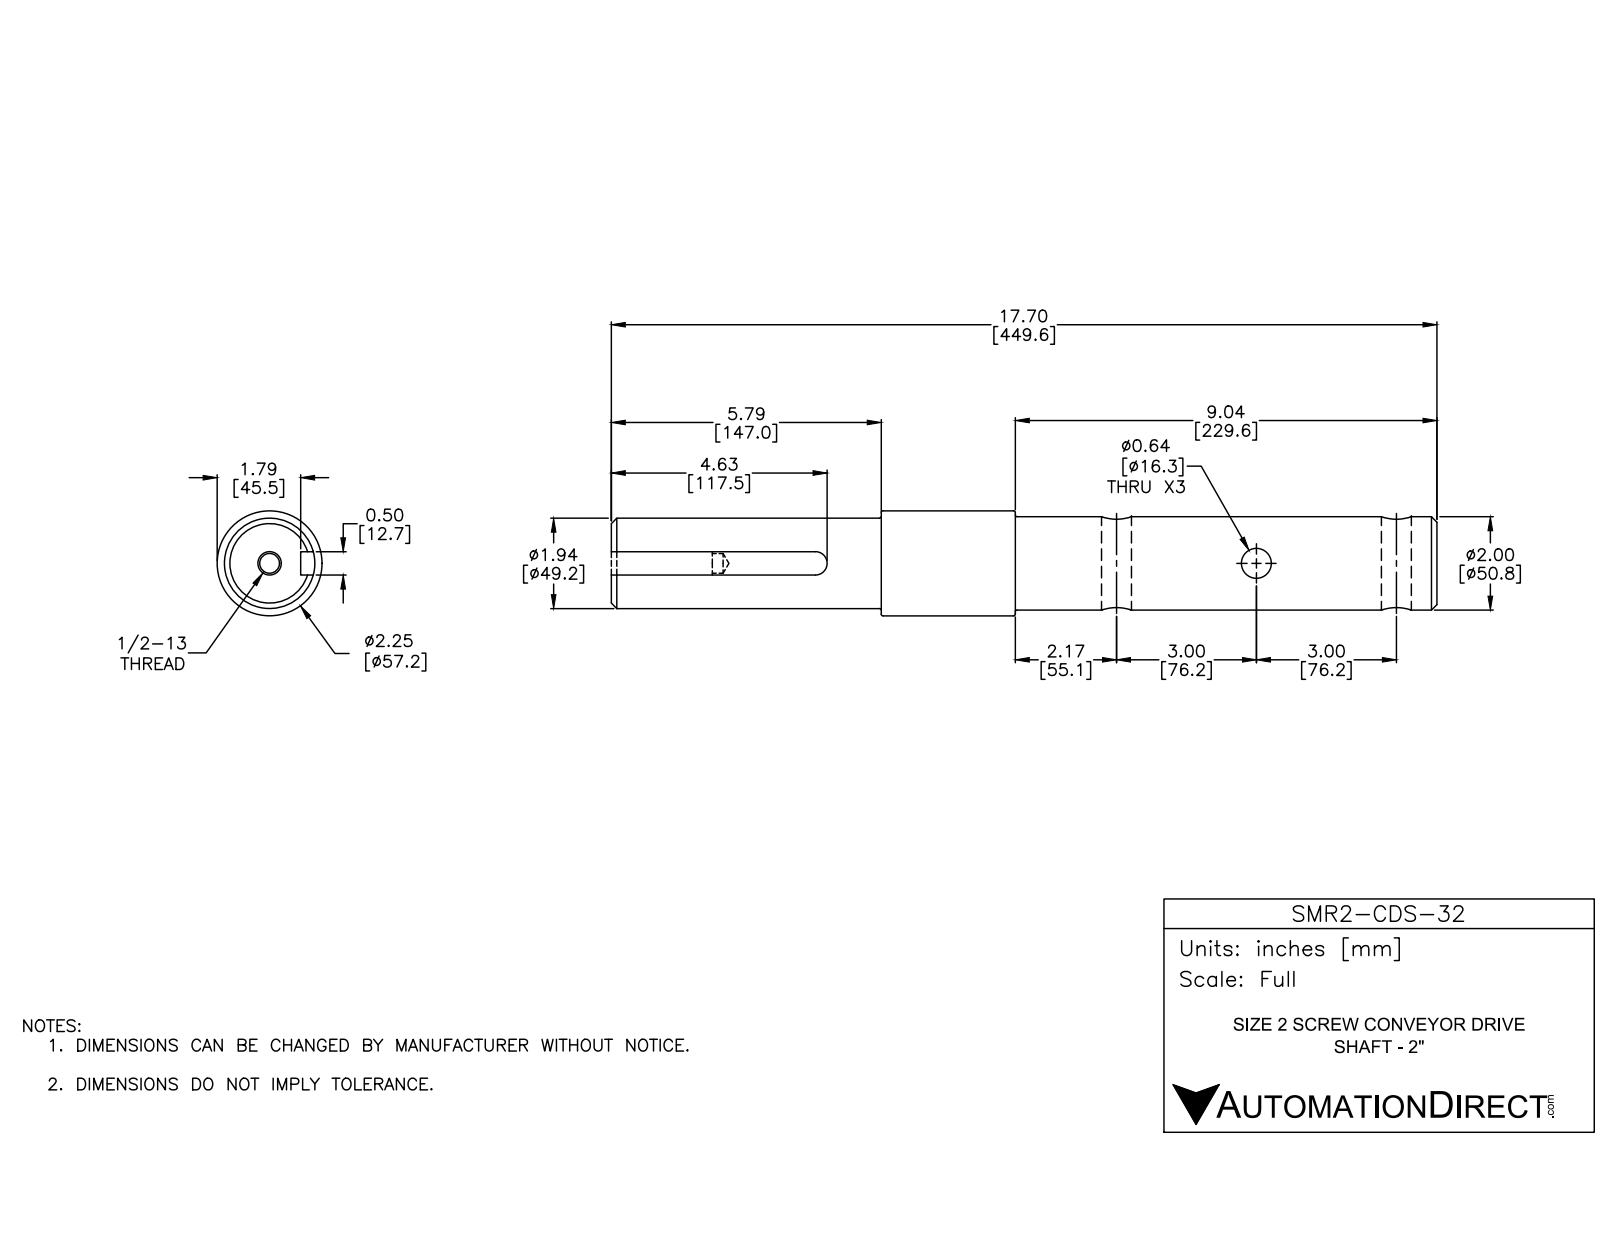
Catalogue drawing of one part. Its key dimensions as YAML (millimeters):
part_name: "SMR2-CDS-32"
step_written_by: "SolidWorks 2016 (AUTOMOTIVE_DESIGN)"
units: millimeters
bodies: {solids: 1, faces: 40, planar: 8, cylindrical: 18, other: 14}
overall_size: [449.6, 57.2, 57.2]
volume: 881000
surface_area: 87030
round_holes:
  - {diameter: 16.3, count: 3}
  - {diameter: 10.7, count: 1}
  - {diameter: 12.7, count: 1}
round_bosses_or_shafts:
  - {diameter: 57.2, count: 1}
  - {diameter: 50.8, count: 1}
  - {diameter: 49.2, count: 1}
partial_cylinders:
  - {radius: 6.4, count: 1}
face_to_face_distances: [449.6, 12.7, 147, 302.6, 220, 73, 229.6, 55, 92, 165]
hole_center_spacings: [152.4]
